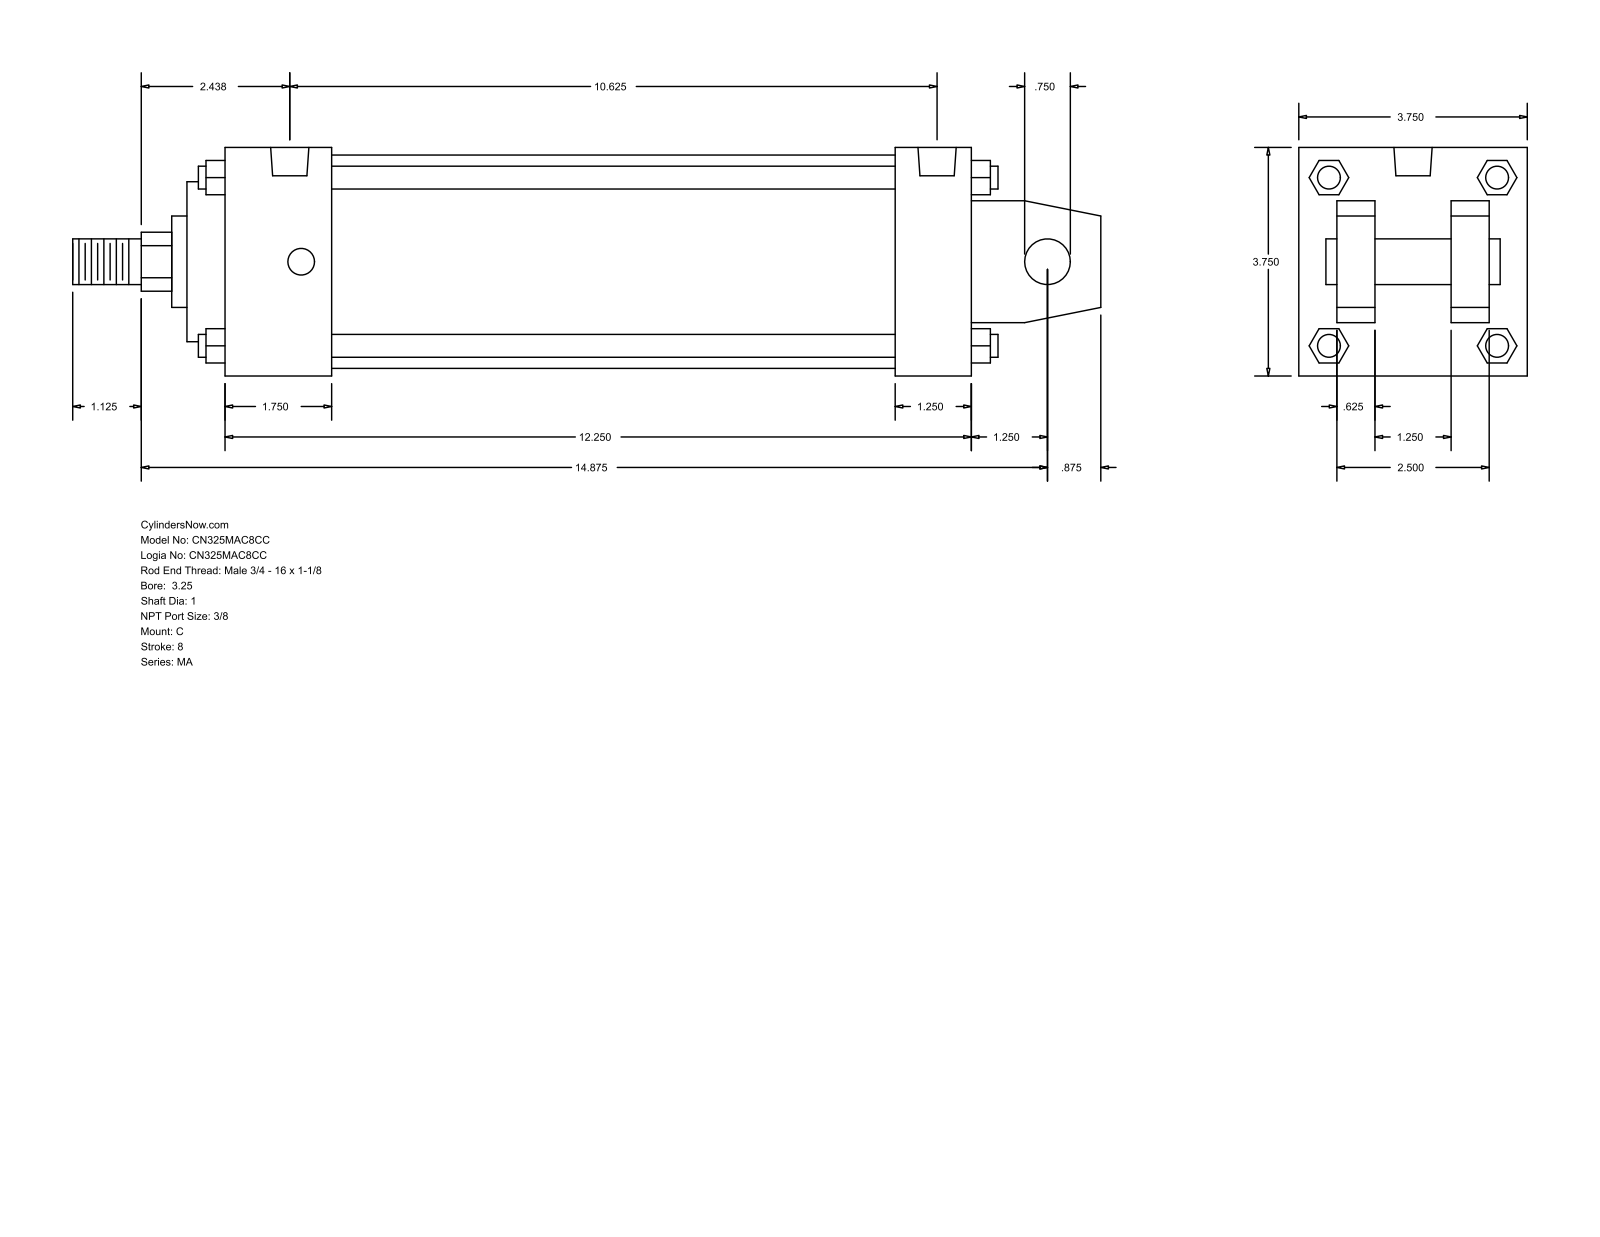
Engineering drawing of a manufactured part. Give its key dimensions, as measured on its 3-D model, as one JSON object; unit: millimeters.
{"part_name": "MA_C__0325_1", "step_written_by": "GSSL Pune (CONFIG_CONTROL_DESIGN)", "units": "millimeters", "bodies": {"solids": 0, "faces": 141, "planar": 109, "cylindrical": 32, "other": 0}, "overall_size": [428.62, 95.25, 95.25], "round_holes": [[11.11, 4], [15.93, 2]], "round_bosses_or_shafts": [[9.53, 4], [19.05, 2], [88.9, 1], [66.67, 1], [38.1, 1], [25.4, 1]], "partial_cylinders_radius": [[12.29, 1]], "face_to_face_distances": [95.24, 15.87, 63.5, 311.15, 31.74, 79.37, 47.63, 327.02, 279.4, 31.75], "hole_center_spacings": [260.35, 4.76, 4.77, 265.11, 265.12, 269.88]}
